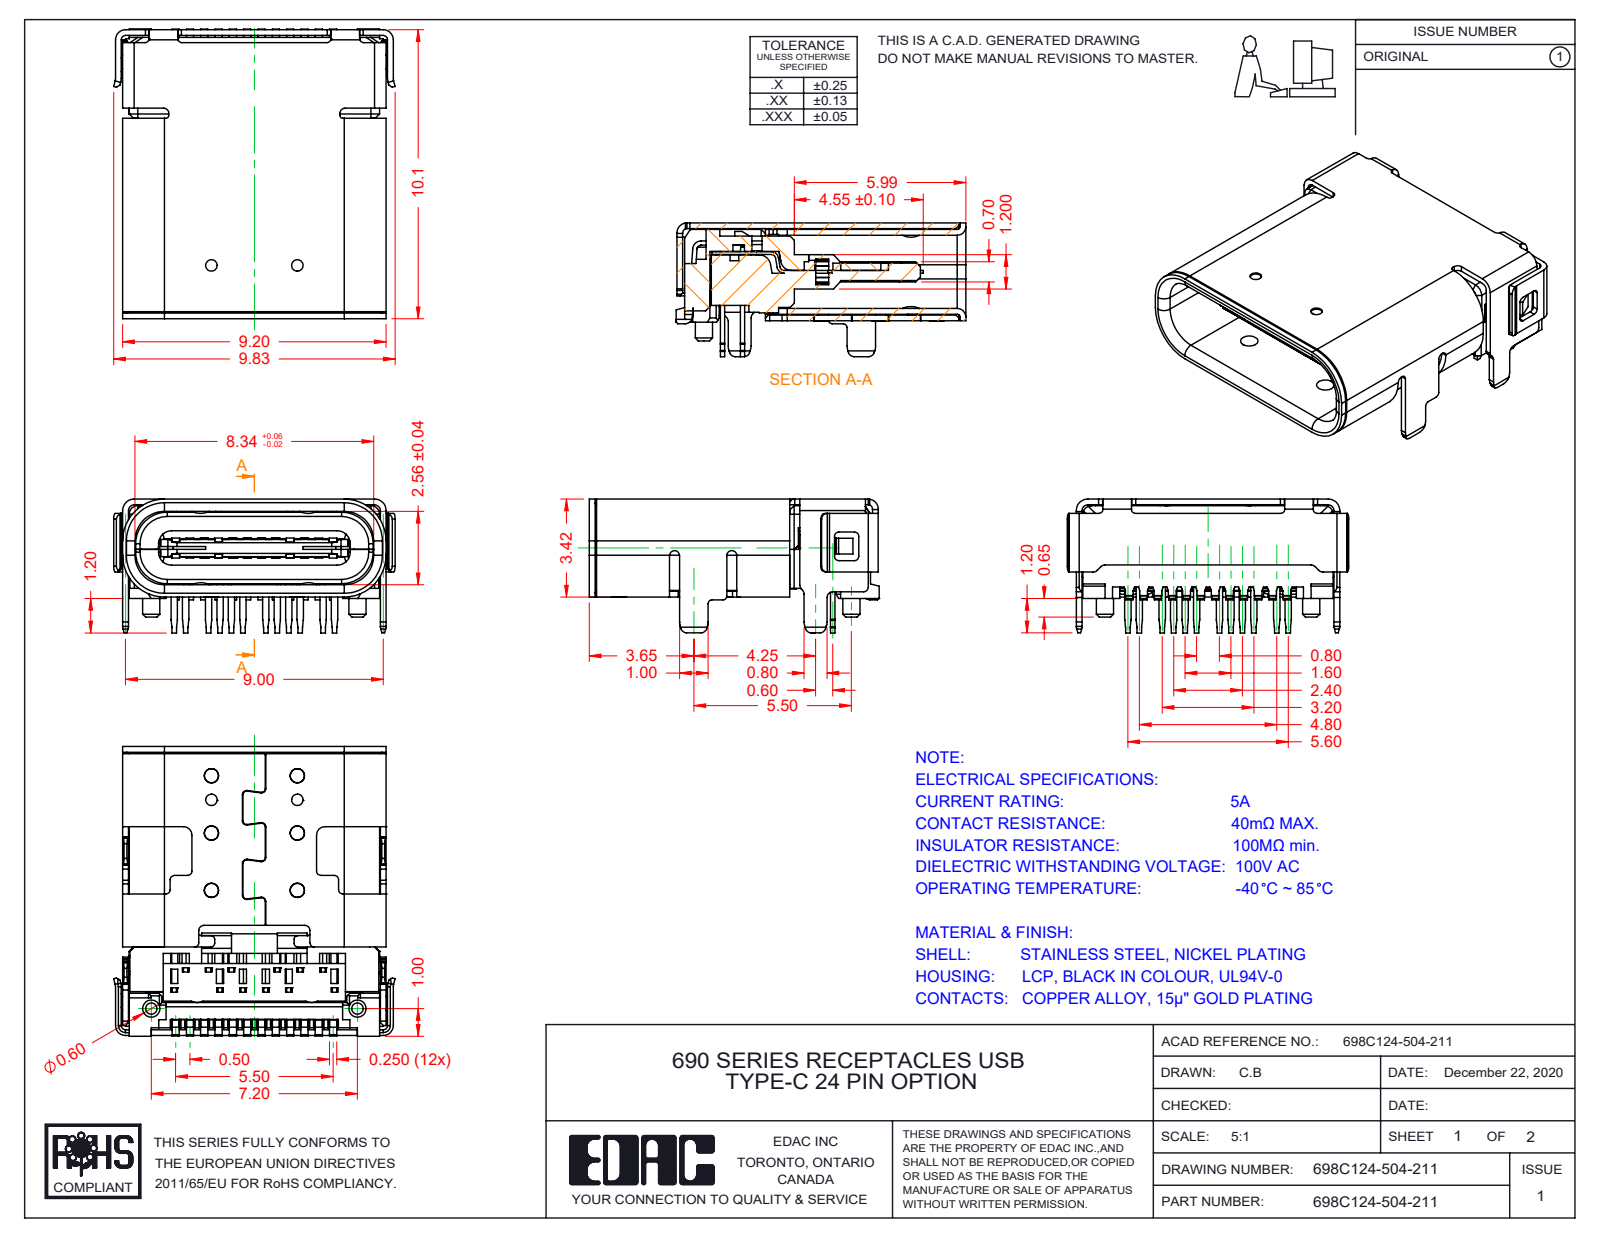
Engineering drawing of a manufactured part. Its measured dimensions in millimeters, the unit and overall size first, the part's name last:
Units: millimetres
Overall size (bounding box): 10.12 × 9.83 × 4.67
Round holes (diameter × count): ⌀0.4 ×2, ⌀0.5 ×2, ⌀0.6 ×2, ⌀0.65 ×2
Round bosses / shafts (diameter × count): ⌀0.5 ×6, ⌀0.6 ×4
Partial cylindrical surfaces — rounded edges, fillets, slot ends (radius × count): R0.15 ×73, R0.3 ×61, R0.1 ×38, R0.2 ×31, R0.13 ×26, R0.35 ×10, R0.17 ×5, R0.25 ×5
Main face-to-face distances: 2.99, 0.4, 0.55, 2.79, 2.76, 0.43, 1.28, 3.19, 0.5, 3.22
Hole centre spacings: 2.07, 3.43, 3.68, 4.53, 5.73, 6.42, 2.5, 2.53
Volume: 167 mm³ · Surface area: 1 504 mm²
Bodies: 27 solids, 3274 faces (2522 planar, 639 cylindrical, 113 other)
Part name (STEP PRODUCT): 698C124-504-211; Contacts 698C124-504-211; Insulator1 698C124-504-211; Insulator2 698C124-504-211 (+1 more)
STEP written by: SolidWorks 2020 (AUTOMOTIVE_DESIGN)
